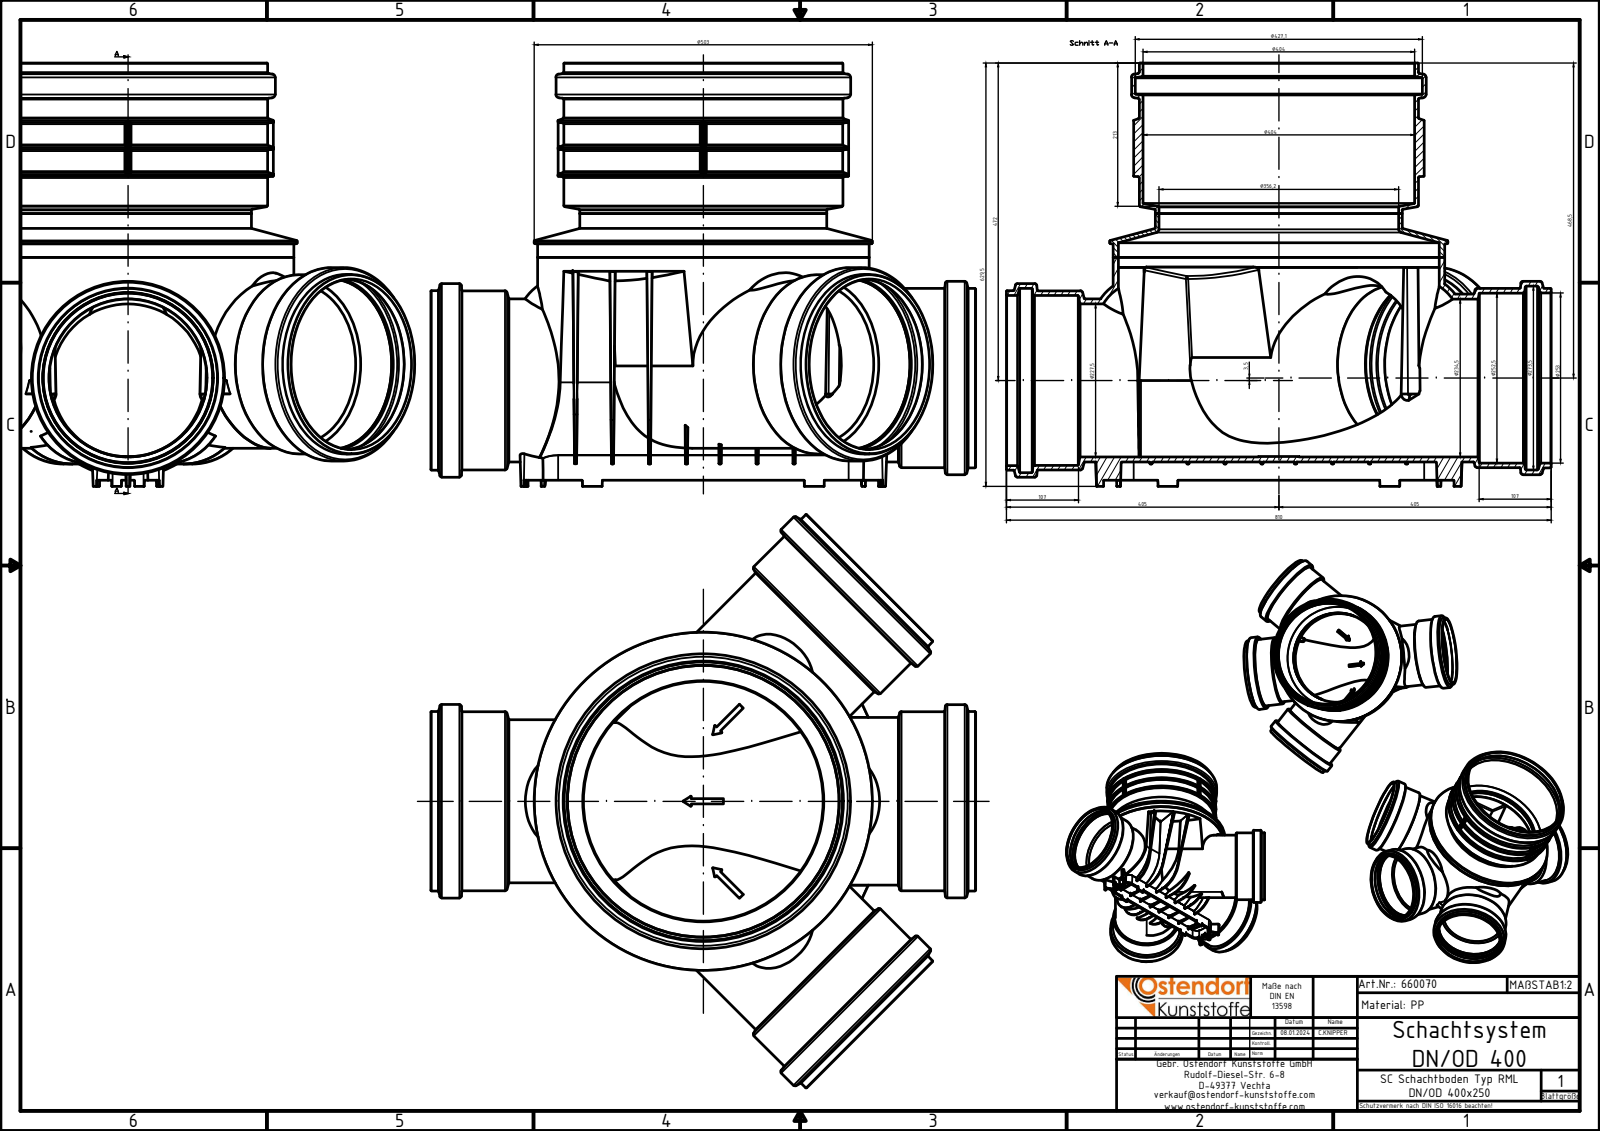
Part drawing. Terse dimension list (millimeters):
name: 660070z; 660070 Teil 1; 660070 Teil 2; 660070 Teil 3
written by: Autodesk Inventor 2024 (AUTOMOTIVE_DESIGN)
unit: mm
bodies: 3 solids, 1349 faces (236 planar, 442 cylindrical, 671 other)
size: 852.65 × 810 × 629.5
volume: 11 590 000 mm³; area: 3 449 000 mm²
holes: 6× ⌀253, 4× ⌀252.5, 3× ⌀234.5, 3× ⌀273.5, 1× ⌀227.5, 1× ⌀274, 1× ⌀356.2, 1× ⌀404, 1× ⌀427.1, 1× ⌀477
bosses: 4× ⌀267, 4× ⌀266.5, 3× ⌀287.5, 3× ⌀249.5, 1× ⌀503, 1× ⌀493, 1× ⌀438.1, 1× ⌀432
rounds: 207× R0.5, 8× R90, 6× R2.75, 2× R5, 2× R124.75, 1× R113.8
face distances: 55, 110, 90.5, 160, 215, 105, 270, 65, 165, 50
hole spacings: 3.5
